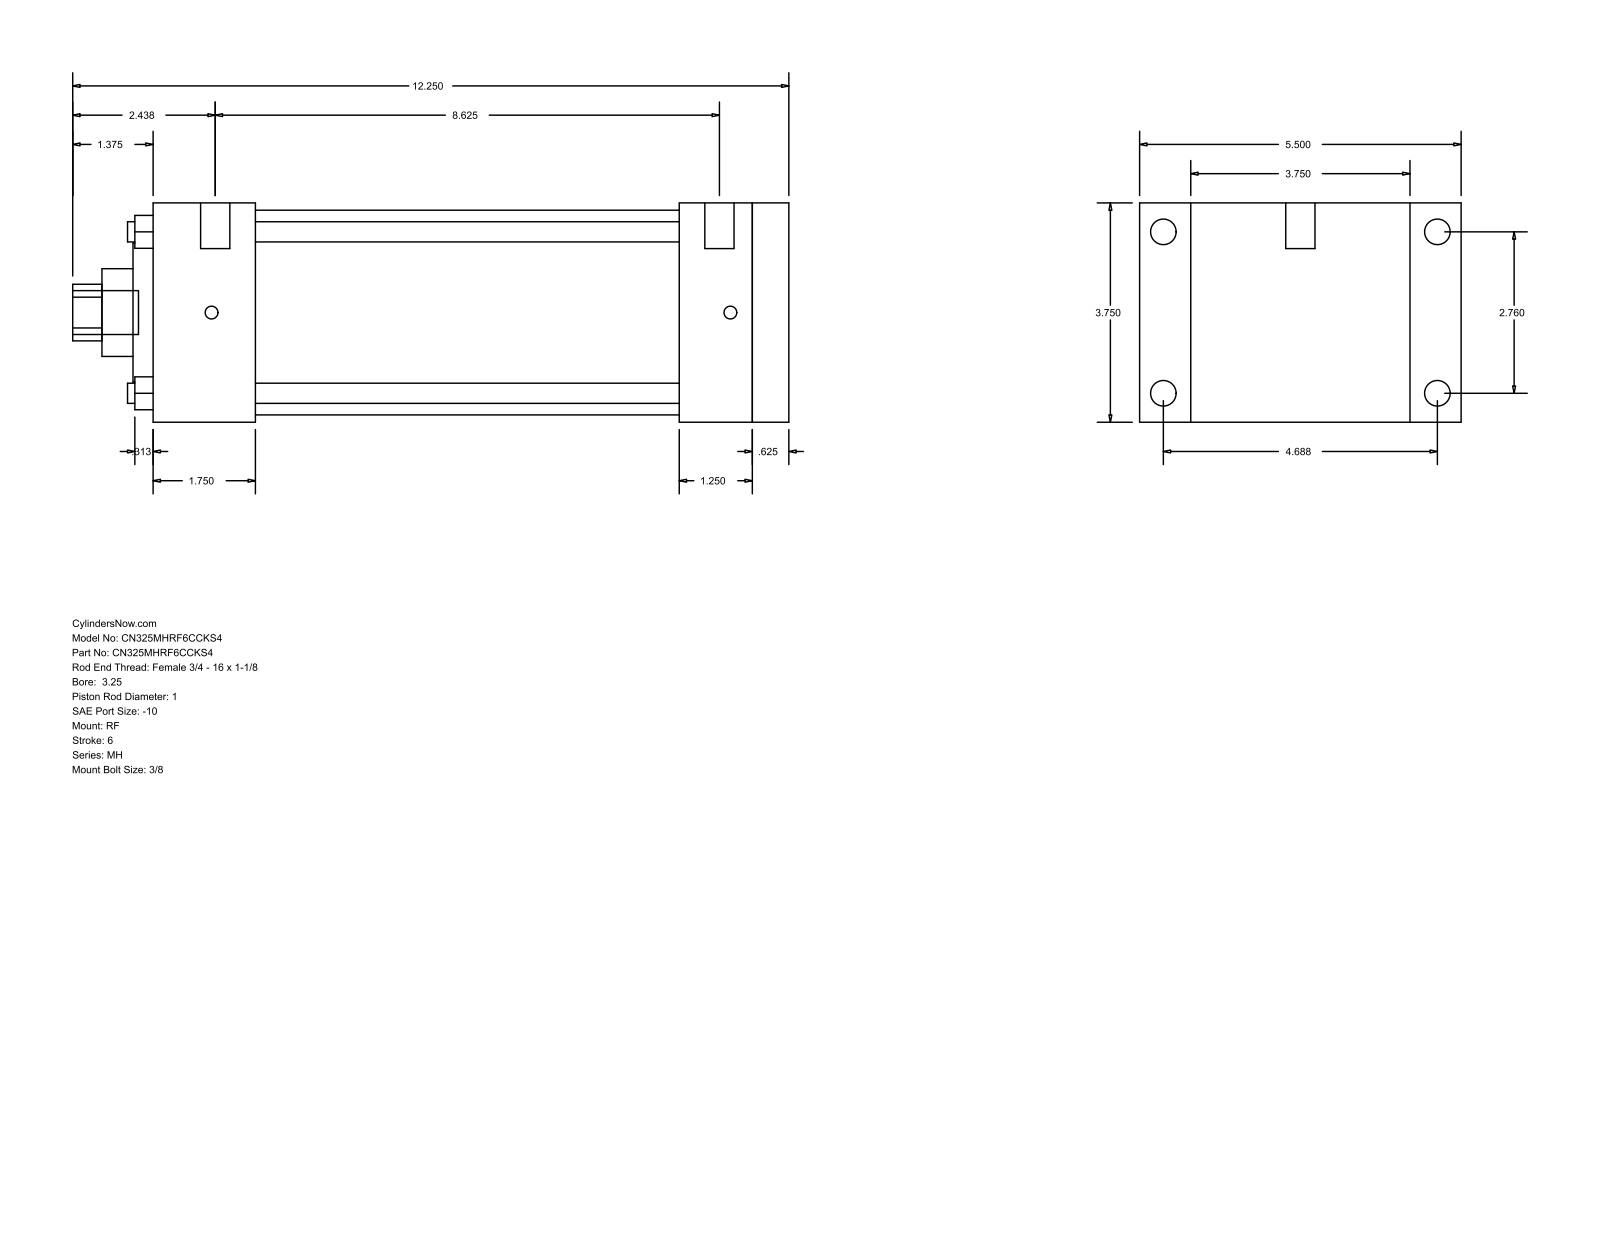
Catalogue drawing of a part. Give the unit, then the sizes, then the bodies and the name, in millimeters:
Units: millimetres
Overall size (bounding box): 311.15 × 139.7 × 95.25
Round holes (diameter × count): ⌀8.76 ×4, ⌀25.4 ×1, ⌀38.1 ×1, ⌀60.33 ×1, ⌀88.9 ×1
Round bosses / shafts (diameter × count): ⌀11.13 ×4, ⌀5.56 ×4, ⌀12.7 ×2, ⌀19.05 ×1
Partial cylindrical surfaces — rounded edges, fillets, slot ends (radius × count): R12.29 ×1
Main face-to-face distances: 95.24, 276.23, 260.35, 15.88, 22.23, 117.47, 44.46, 215.89, 231.77, 228.6
Hole centre spacings: 49.57, 70.1, 99.14
Bodies: 0 solids, 94 faces (65 planar, 29 cylindrical, 0 other)
Part name (STEP PRODUCT): MH_RF__0325_1
STEP written by: GSSL Pune (CONFIG_CONTROL_DESIGN)
